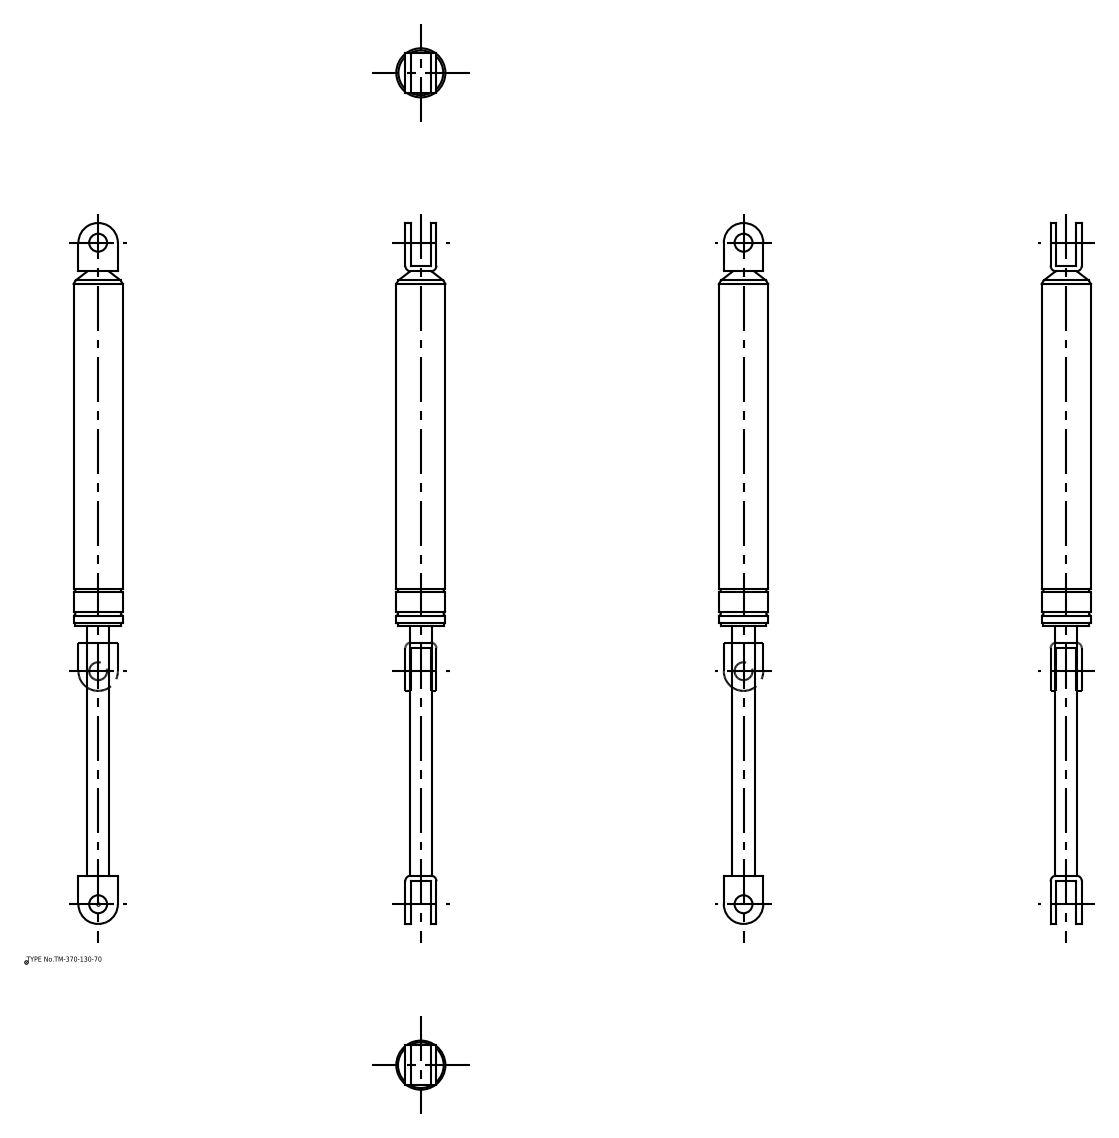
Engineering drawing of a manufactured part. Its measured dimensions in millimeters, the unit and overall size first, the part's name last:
Units: millimetres
Overall size (bounding box): 391 × 28.2 × 28.2
Round holes (diameter × count): ⌀10 ×2
Round bosses / shafts (diameter × count): ⌀28.2 ×1, ⌀27.4 ×1, ⌀25.5 ×1, ⌀12.5 ×1
Partial cylindrical surfaces — rounded edges, fillets, slot ends (radius × count): R3.2 ×4, R11 ×2
Main face-to-face distances: 3.2, 14.2, 17.4, 11, 22, 340.2, 142.2, 343.4, 201.2, 198
Hole centre spacings: 369
Volume: 139 499 mm³ · Surface area: 29 284 mm²
Bodies: 2 solids, 64 faces (22 planar, 32 cylindrical, 10 other)
Part name (STEP PRODUCT): TM_370_130_70; TM_370_130_70_div
STEP written by: spGate 16.7.1 (AUTOMOTIVE_DESIGN)
